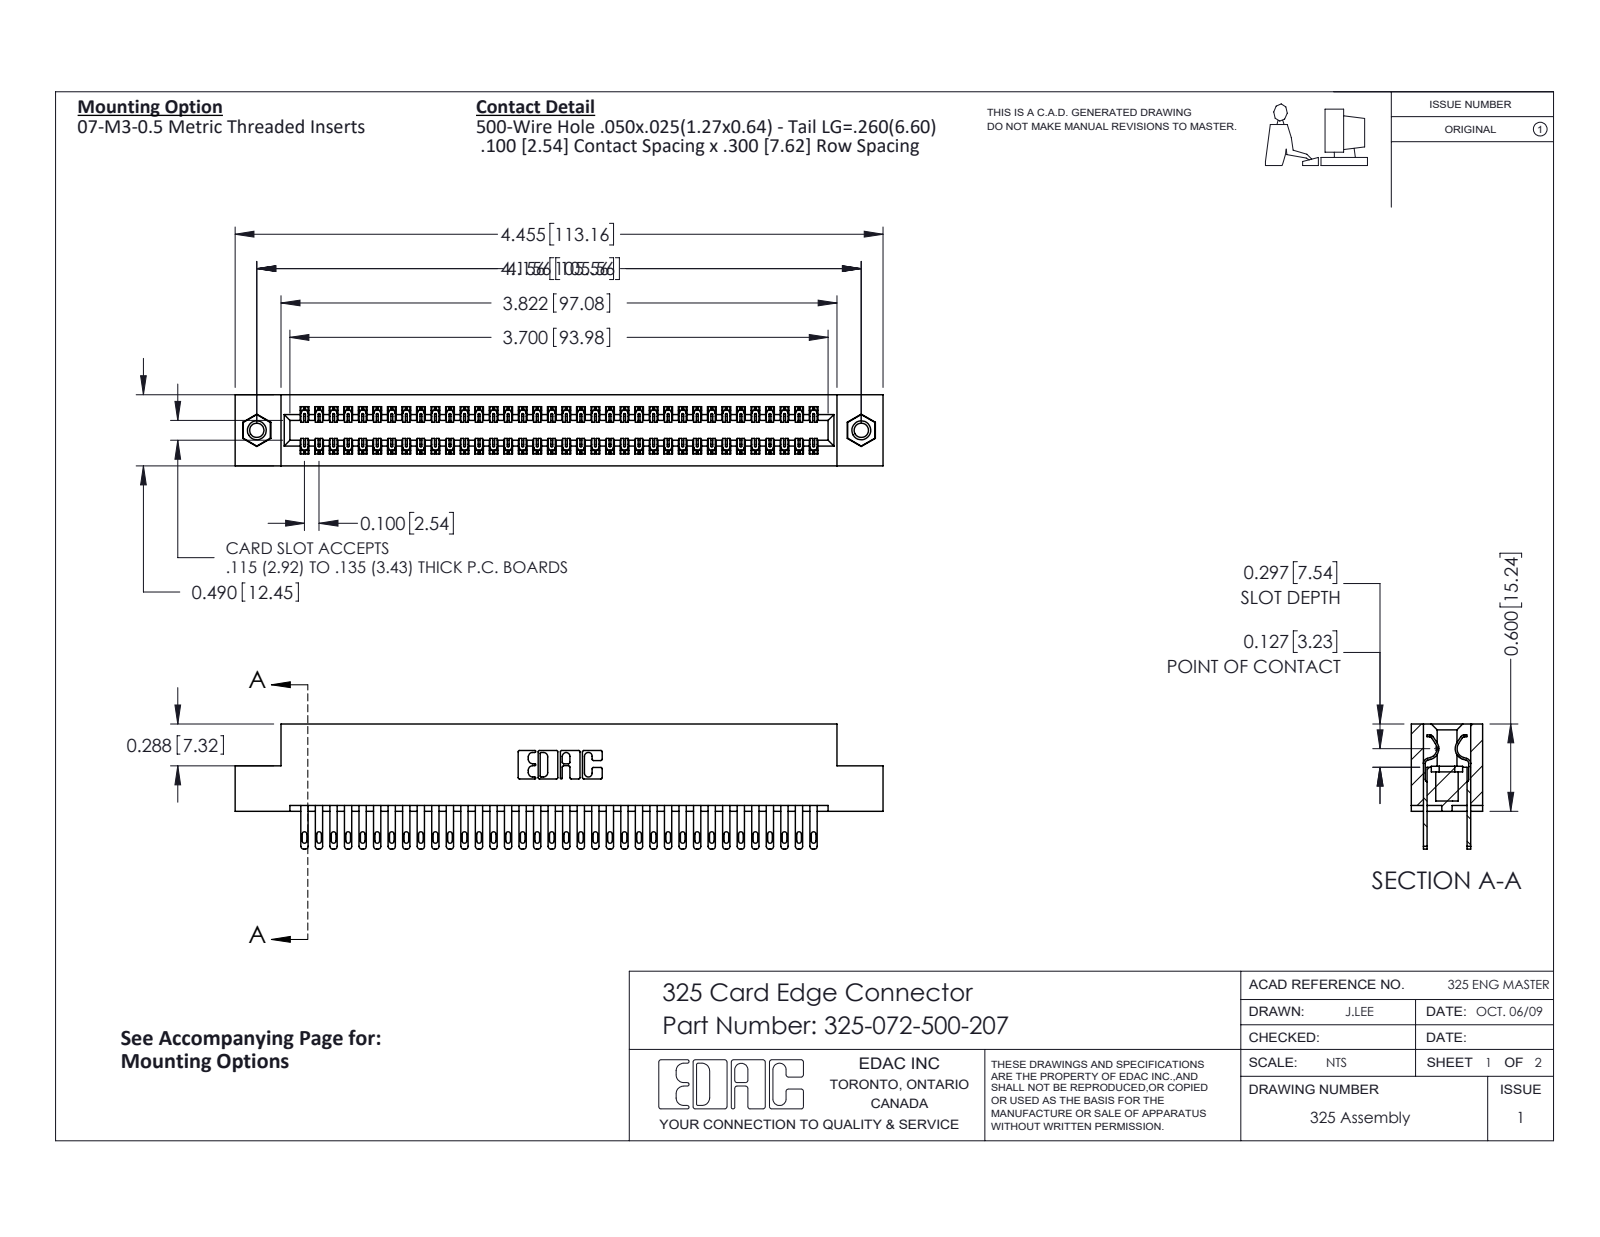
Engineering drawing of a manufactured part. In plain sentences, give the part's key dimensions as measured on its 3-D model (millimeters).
The part is named "345-250-001_345-250-005-103; 325 Part_TI; 325-072-500-207; 325-292-001_325-293-100". Its 3-D file was written by "SolidWorks 2016 (CONFIG_CONTROL_DESIGN)". It is 75 solids with 3630 faces: 2262 planar, 1352 cylindrical and 16 other. Overall it measures 113.2 by 21.8 by 12.4 millimeters. Its volume is 14 800 cubic millimeters and its surface area 18 500 square millimeters. Round holes: 2 of diameter 2.5, 2 of diameter 3.2, 2 of diameter 4.1. Round bosses or shafts: 2 of diameter 3.9. Partial cylindrical surfaces (rounded edges, fillets, slot ends): 108 of radius 0.2, 72 of radius 0.4, 72 of radius 0.5, 22 of radius 0.3, 6 of radius 0.2, 6 of radius 0.8, 3 of radius 0.7, 2 of radius 0.4. The main face-to-face distances are 2.1, 10.3, 7.6, 2.7, 9.7, 0.6, 12.4, 8.3, 7, 14.2. The hole center spacings are 105.6.
